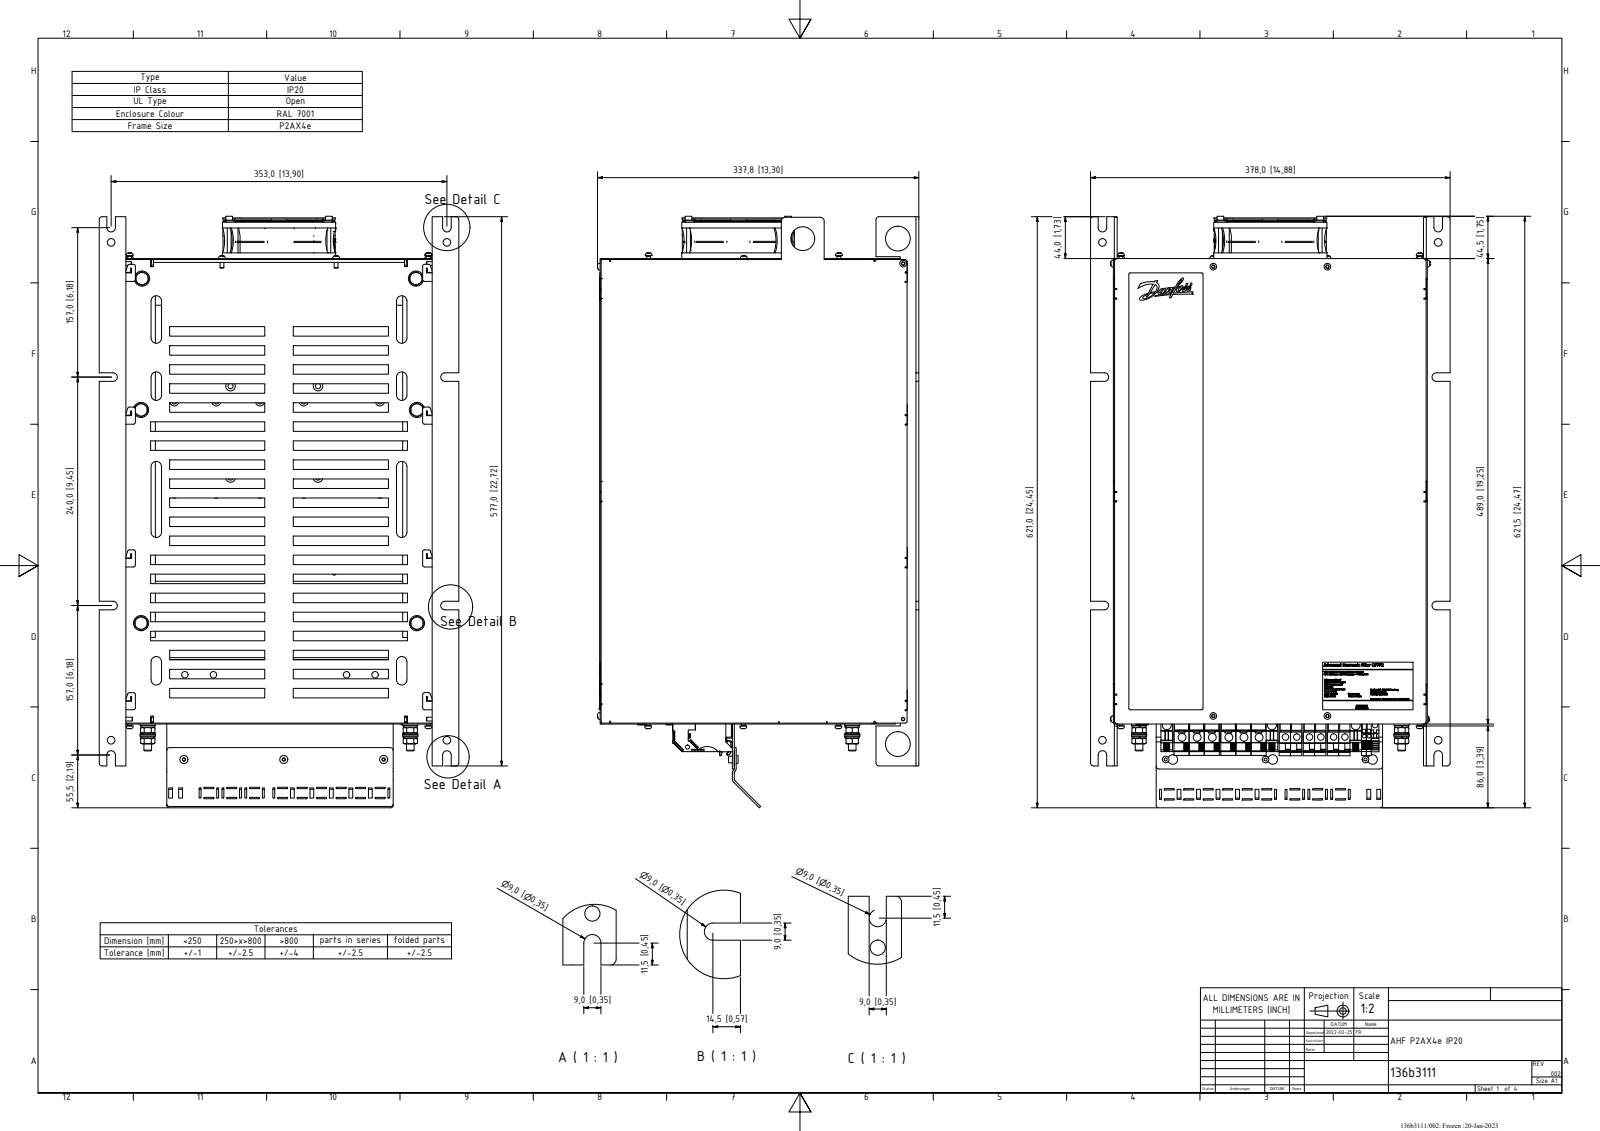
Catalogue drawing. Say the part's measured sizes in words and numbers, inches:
The part is named "X4_IP20_EF_OUT_1". Its 3-D file was written by "CREO PARAMETRIC BY PTC INC, 2020342 (CONFIG_CONTROL_DESIGN)". It is 10 solids with 2262 faces: 1730 planar, 479 cylindrical and 53 other. Overall it measures 24.467 by 14.882 by 13.299 inches. Its volume is 215.7 cubic inches and its surface area 2 987 square inches. Round holes: 6 of diameter 0.268, 6 of diameter 0.325, 4 of diameter 0.315, 2 of diameter 0.157, 2 of diameter 0.37, 2 of diameter 0.492, 2 of diameter 1.024, 1 of diameter 0.984, 1 of diameter 1.339, 1 of diameter 1.881, 1 of diameter 2.228, 1 of diameter 2.441. Round bosses or shafts: 18 of diameter 0.276, 4 of diameter 0.193, 3 of diameter 0.593, 3 of diameter 0.583, 3 of diameter 0.354, 2 of diameter 0.512, 2 of diameter 0.445, 2 of diameter 0.315. Partial cylindrical surfaces (rounded edges, fillets, slot ends): 8 of radius 0.177, 1 of radius 0.051, 1 of radius 0.079, 1 of radius 0.114, 1 of radius 0.144, 1 of radius 0.154, 1 of radius 0.157, 1 of radius 0.168. The main face-to-face distances are 0.118, 0.157, 12.835, 12.126, 12.677, 12.992, 0.079, 12.008, 12.244, 19.173. The hole center spacings are 0.626, 0.996, 0.469, 1.937, 0.528, 1.252, 1.311, 1.465.
